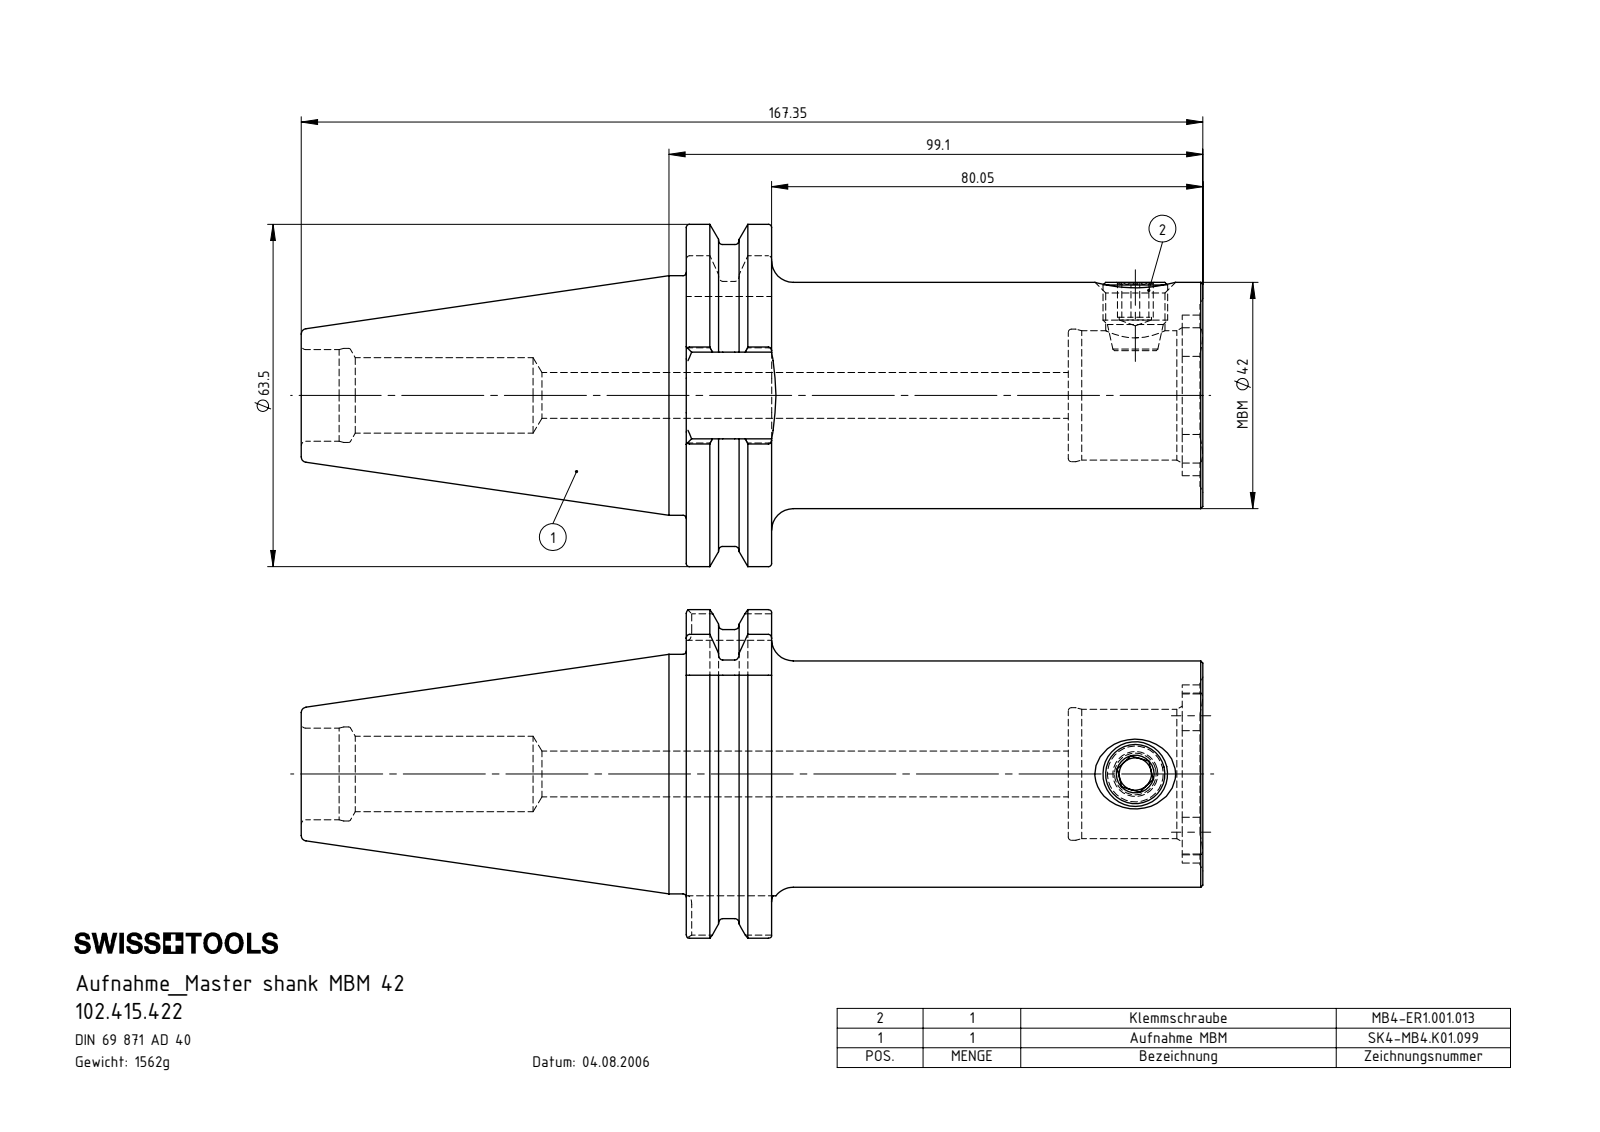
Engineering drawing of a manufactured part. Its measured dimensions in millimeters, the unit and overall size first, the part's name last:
Units: millimetres
Overall size (bounding box): 167.35 × 63.5 × 60.94
Round holes (diameter × count): ⌀6 ×1, ⌀8.5 ×1, ⌀11 ×1, ⌀14 ×1, ⌀17 ×1, ⌀17.45 ×1, ⌀24 ×1, ⌀24.6 ×1
Round bosses / shafts (diameter × count): ⌀44.45 ×1, ⌀42 ×1, ⌀12 ×1
Partial cylindrical surfaces — rounded edges, fillets, slot ends (radius × count): R1.6 ×8, R4.2 ×4, R14.9 ×1, R16.52 ×1, R28 ×1, R31.75 ×1
Main face-to-face distances: 15.85, 70.9, 55.05, 92.05, 76.2, 21.15, 3.85, 95.9, 80.05, 25
Volume: 199 016 mm³ · Surface area: 34 067 mm²
Bodies: 2 solids, 170 faces (56 planar, 50 cylindrical, 64 other)
Part name (STEP PRODUCT): SK4-MB4.K01.099_C; 102.415.422; MB4-ER1.001.013_A
STEP written by: SolidWorks 2017 (CONFIG_CONTROL_DESIGN)
